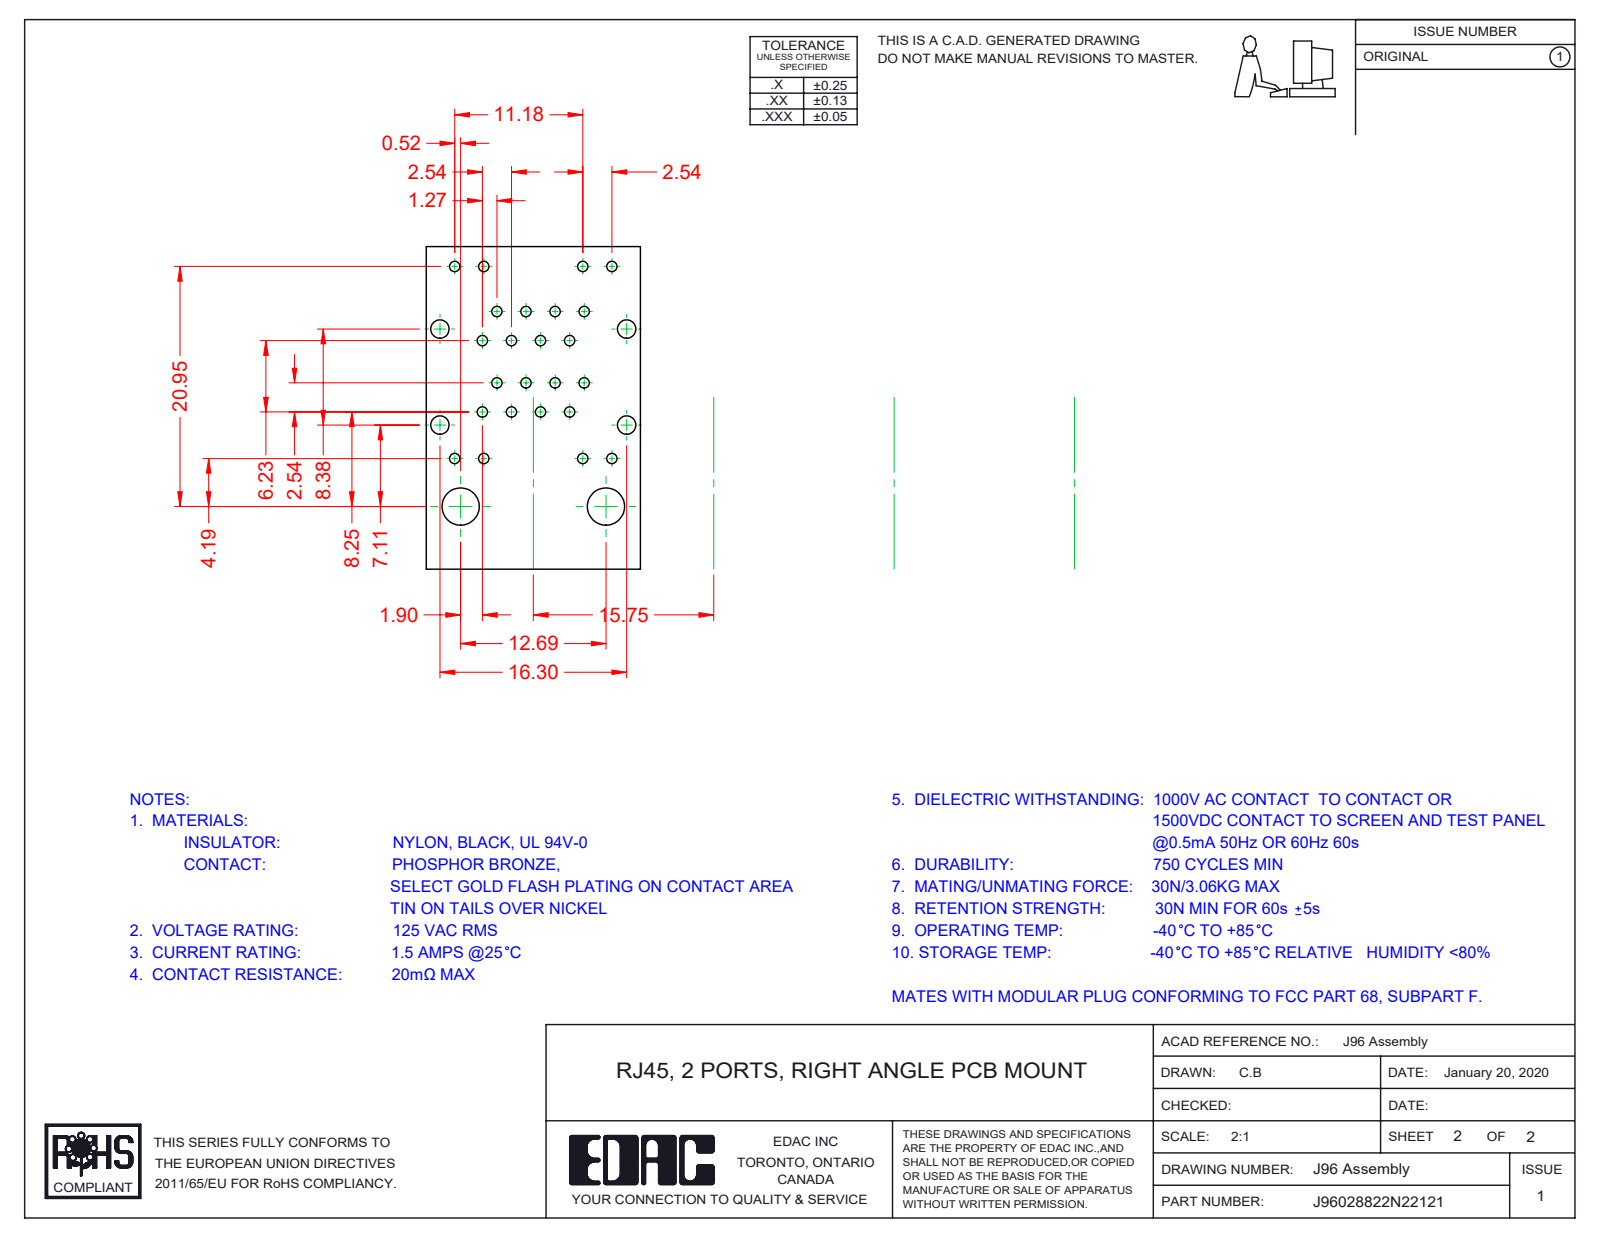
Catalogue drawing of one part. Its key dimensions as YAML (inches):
part_name: "96 LED RH Upper_2-Red; 96 LED LH Upper_2-Red; 96 Insulator Insert; 96 Grounding_2 Ports (+8 more)"
step_written_by: "SolidWorks 2016 (CONFIG_CONTROL_DESIGN)"
units: inches
bodies: {solids: 27, faces: 2382, planar: 1849, cylindrical: 427, other: 106}
overall_size: [1.165, 1.129, 0.661]
volume: 0.418
surface_area: 29.62
partial_cylinders:
  - {radius: 0.01, count: 48}
  - {radius: 0.006, count: 32}
  - {radius: 0.014, count: 24}
  - {radius: 0.02, count: 16}
  - {radius: 0.039, count: 16}
  - {radius: 0.008, count: 13}
  - {radius: 0.028, count: 9}
  - {radius: 0.079, count: 5}
face_to_face_distances: [0.642, 0.634, 0.069, 0.65, 0.581, 0.061, 0.573, 0.021, 0.058, 0.441]
